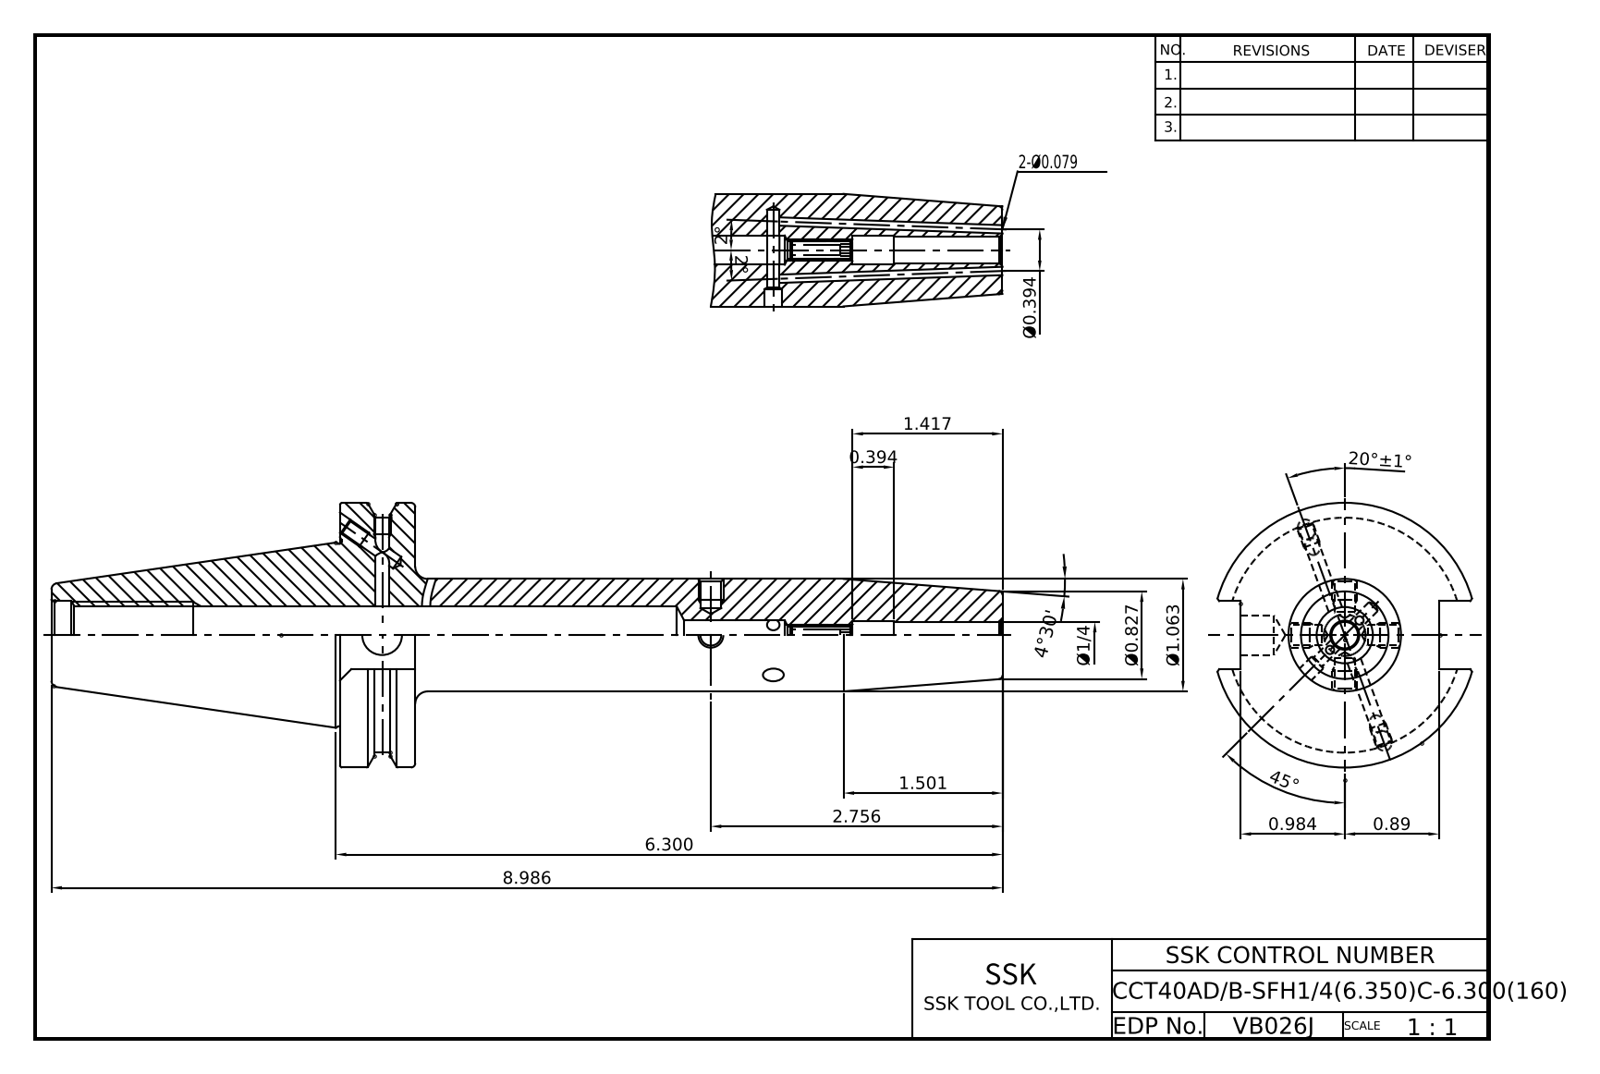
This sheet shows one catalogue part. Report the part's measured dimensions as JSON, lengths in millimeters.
{"part_name": "LO CCT40ADB-SFH6.35C-6.30", "step_written_by": "Autodesk Inventor 2022 (AUTOMOTIVE_DESIGN)", "units": "millimeters", "bodies": {"solids": 1, "faces": 112, "planar": 38, "cylindrical": 39, "other": 35}, "overall_size": [228.25, 63.5, 61.09], "volume_mm3": 167616, "surface_area_mm2": 37758, "round_holes": [[3.24, 4], [4, 3], [2.5, 2], [4.2, 2], [4.92, 2], [3, 1], [4.3, 1], [6.35, 1], [7, 1], [7.55, 1], [9.53, 1], [13, 1]], "round_bosses_or_shafts": [[63.5, 1], [43.8, 1], [27, 1]], "partial_cylinders_radius": [[28.15, 1]], "face_to_face_distances": [18.05, 159, 140.95, 47.6, 16.38, 69.25, 87.3, 228.25, 81.34, 12.09], "hole_center_spacings": [106.82]}
